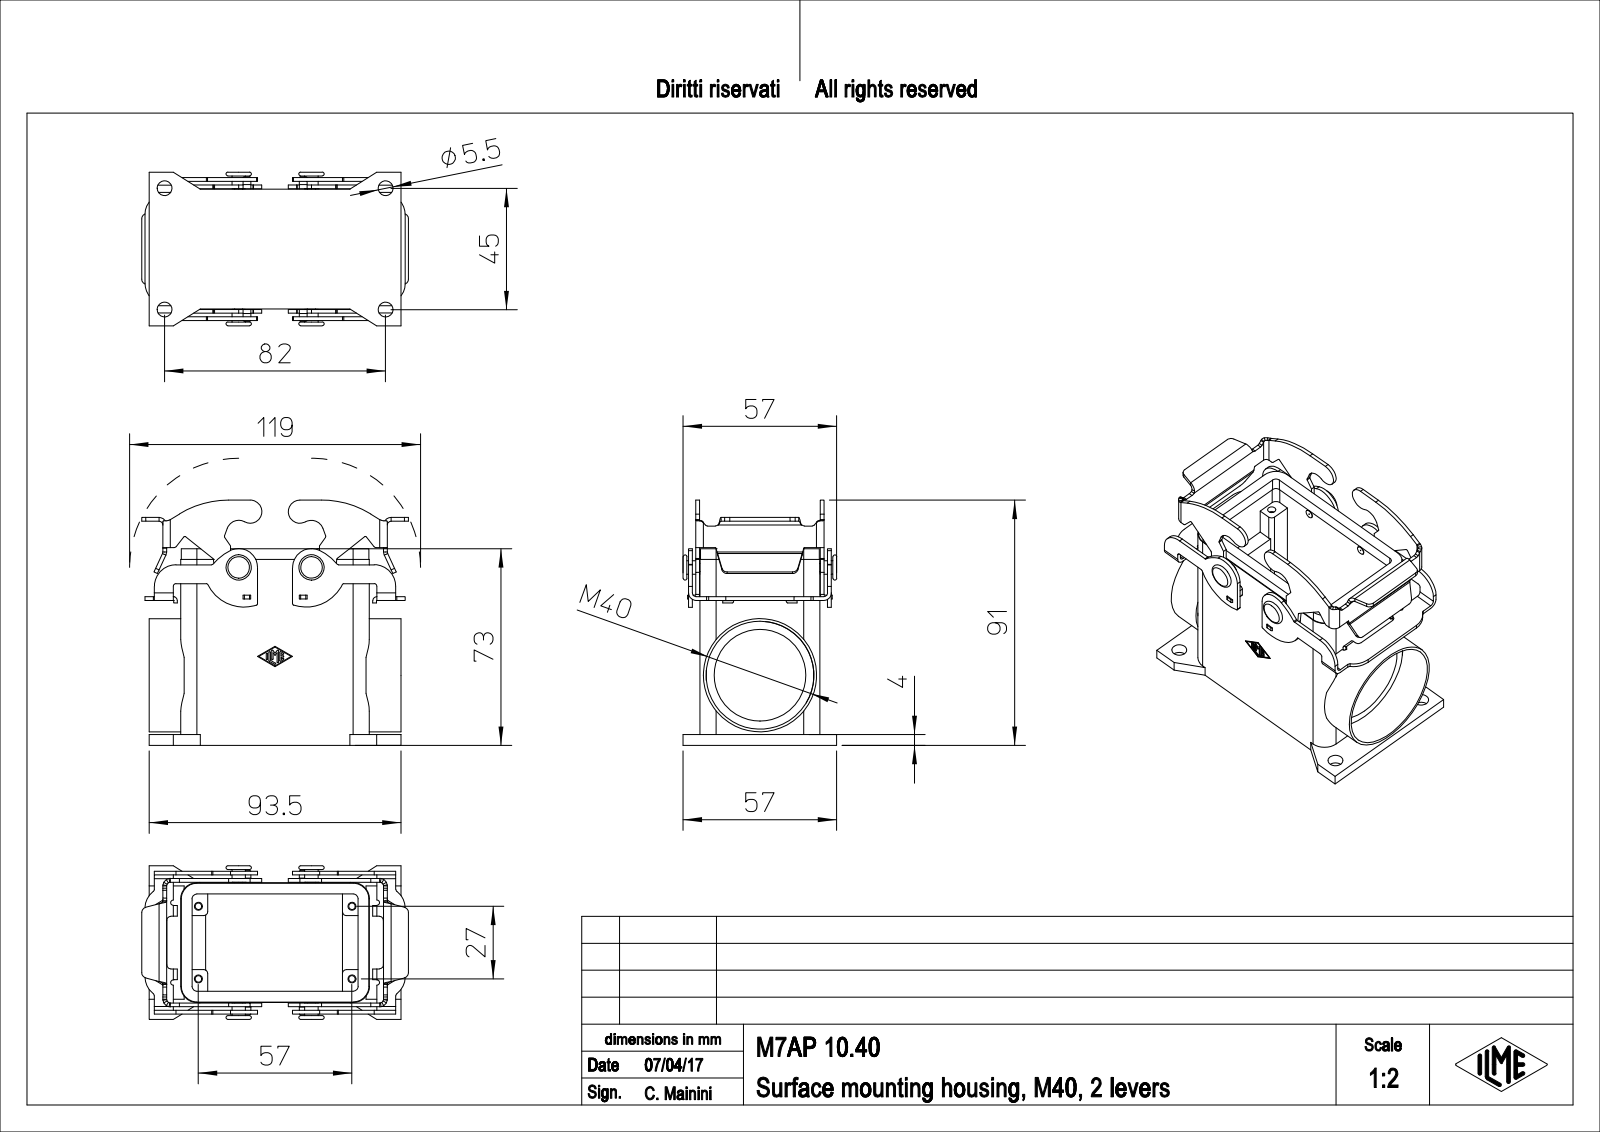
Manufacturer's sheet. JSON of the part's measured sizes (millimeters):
{"part_name": "M7AP_10.40", "step_written_by": "PTC Creo Elements/Direct Modeling 19.0E 27-Jun-2016 (C) Parametric Technology GmbH (AUTOMOTIVE_DESIGN)", "units": "millimeters", "bodies": {"solids": 1, "faces": 613, "planar": 299, "cylindrical": 270, "other": 44}, "overall_size": [98.97, 91, 57], "volume_mm3": 91904, "surface_area_mm2": 61436, "round_holes": [[2.46, 4], [3, 4], [5.5, 4], [3.5, 2], [34, 1], [40, 1]], "round_bosses_or_shafts": [[5, 2], [3.2, 2], [3, 2], [42, 1]], "partial_cylinders_radius": [[0.5, 22], [1, 18], [0.25, 16], [1.5, 14], [2, 12], [1.4, 10], [2.8, 10], [8, 6]], "face_to_face_distances": [4, 40.5, 1.4, 44.5, 2.7, 48.9, 36.5, 8.25, 4.25, 1.55], "hole_center_spacings": [15.4, 38.11, 70.08, 78.27, 27, 45, 57, 63.07]}
